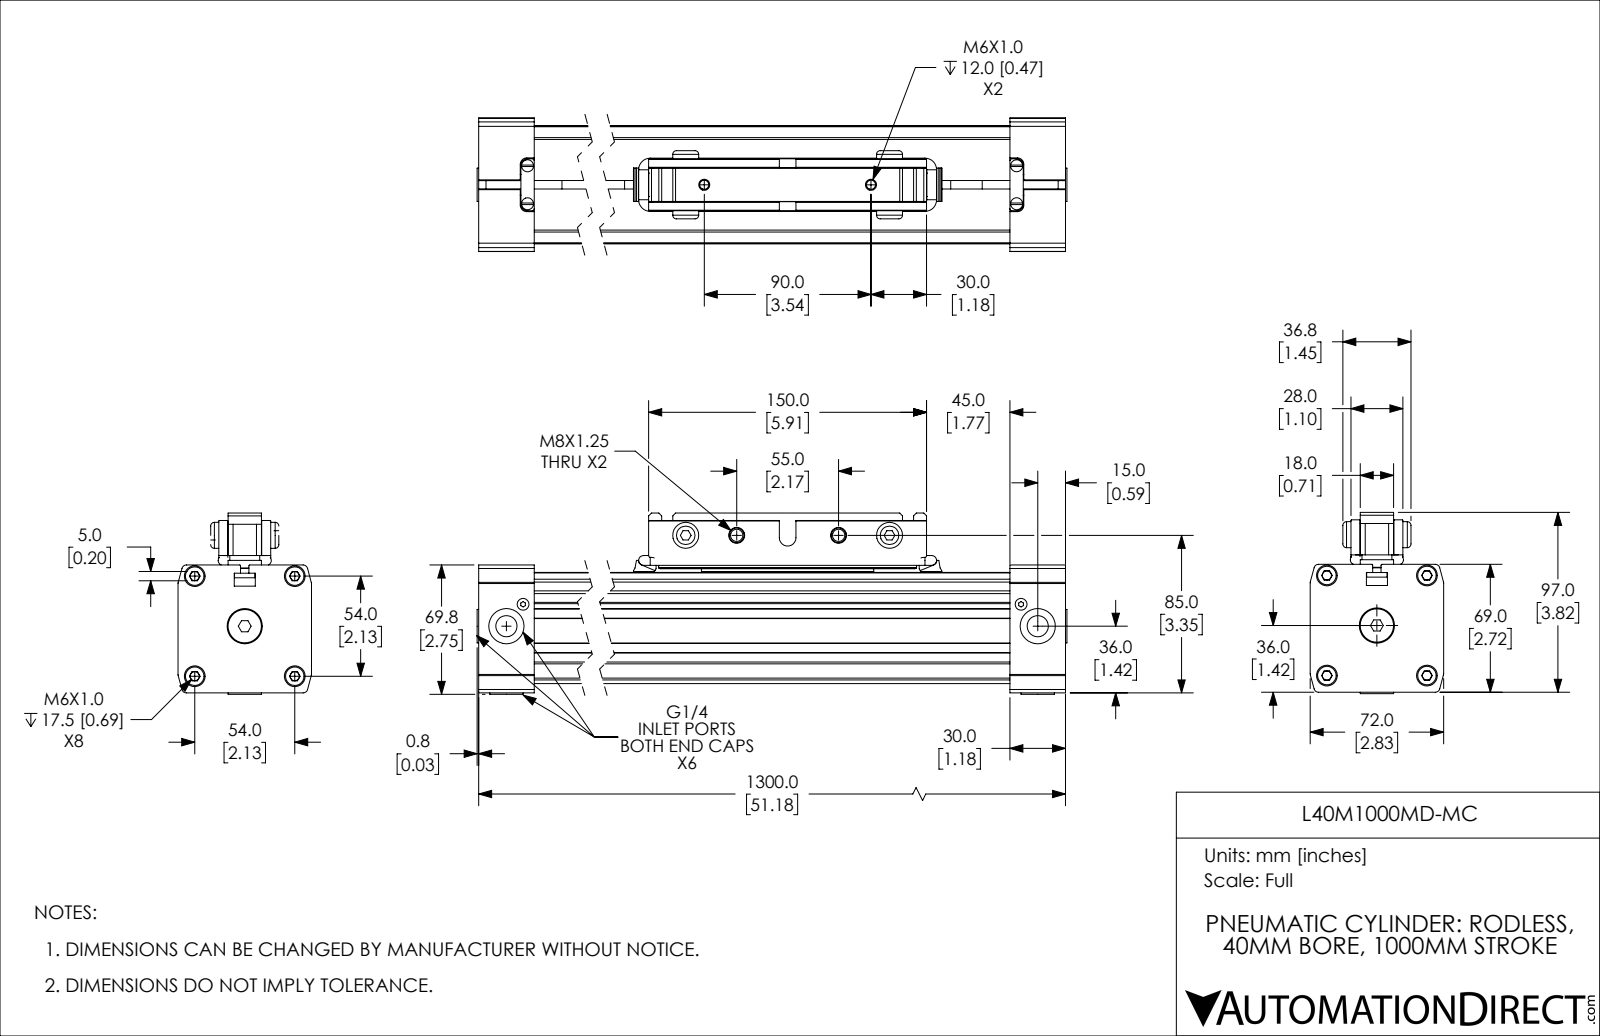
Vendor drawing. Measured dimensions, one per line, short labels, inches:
name: L40M1000MD-MC; L40M1000MD-MC_PISTON; L40M1000MD-MC_BODY
written by: SolidWorks 2019 (CONFIG_CONTROL_DESIGN)
unit: in
bodies: 13 solids, 821 faces (451 planar, 278 cylindrical, 92 other)
size: 51.243 × 3.85 × 2.835
volume: 198.8 in³; area: 1 065 in²
holes: 6× ⌀0.194, 5× ⌀0.451, 5× ⌀0.748, 4× ⌀0.256, 4× ⌀0.262, 4× ⌀0.339, 4× ⌀0.441, 2× ⌀0.252, 1× ⌀1.583
bosses: 4× ⌀0.394, 4× ⌀0.21, 3× ⌀0.709, 3× ⌀0.437, 2× ⌀0.551, 2× ⌀0.518, 1× ⌀1.575, 1× ⌀0.518
rounds: 30× R0.039, 10× R0.079, 8× R0.012, 8× R0.098, 8× R0.138, 4× R0.157, 2× R0.006, 2× R0.008
face distances: 2.362, 0.201, 2.504, 2.303, 0.732, 0.274, 1.45, 0.031, 1.161, 1.343
hole spacings: 0.604, 1.503, 2.126, 49.553, 0.584, 0.807, 1.083, 1.428
